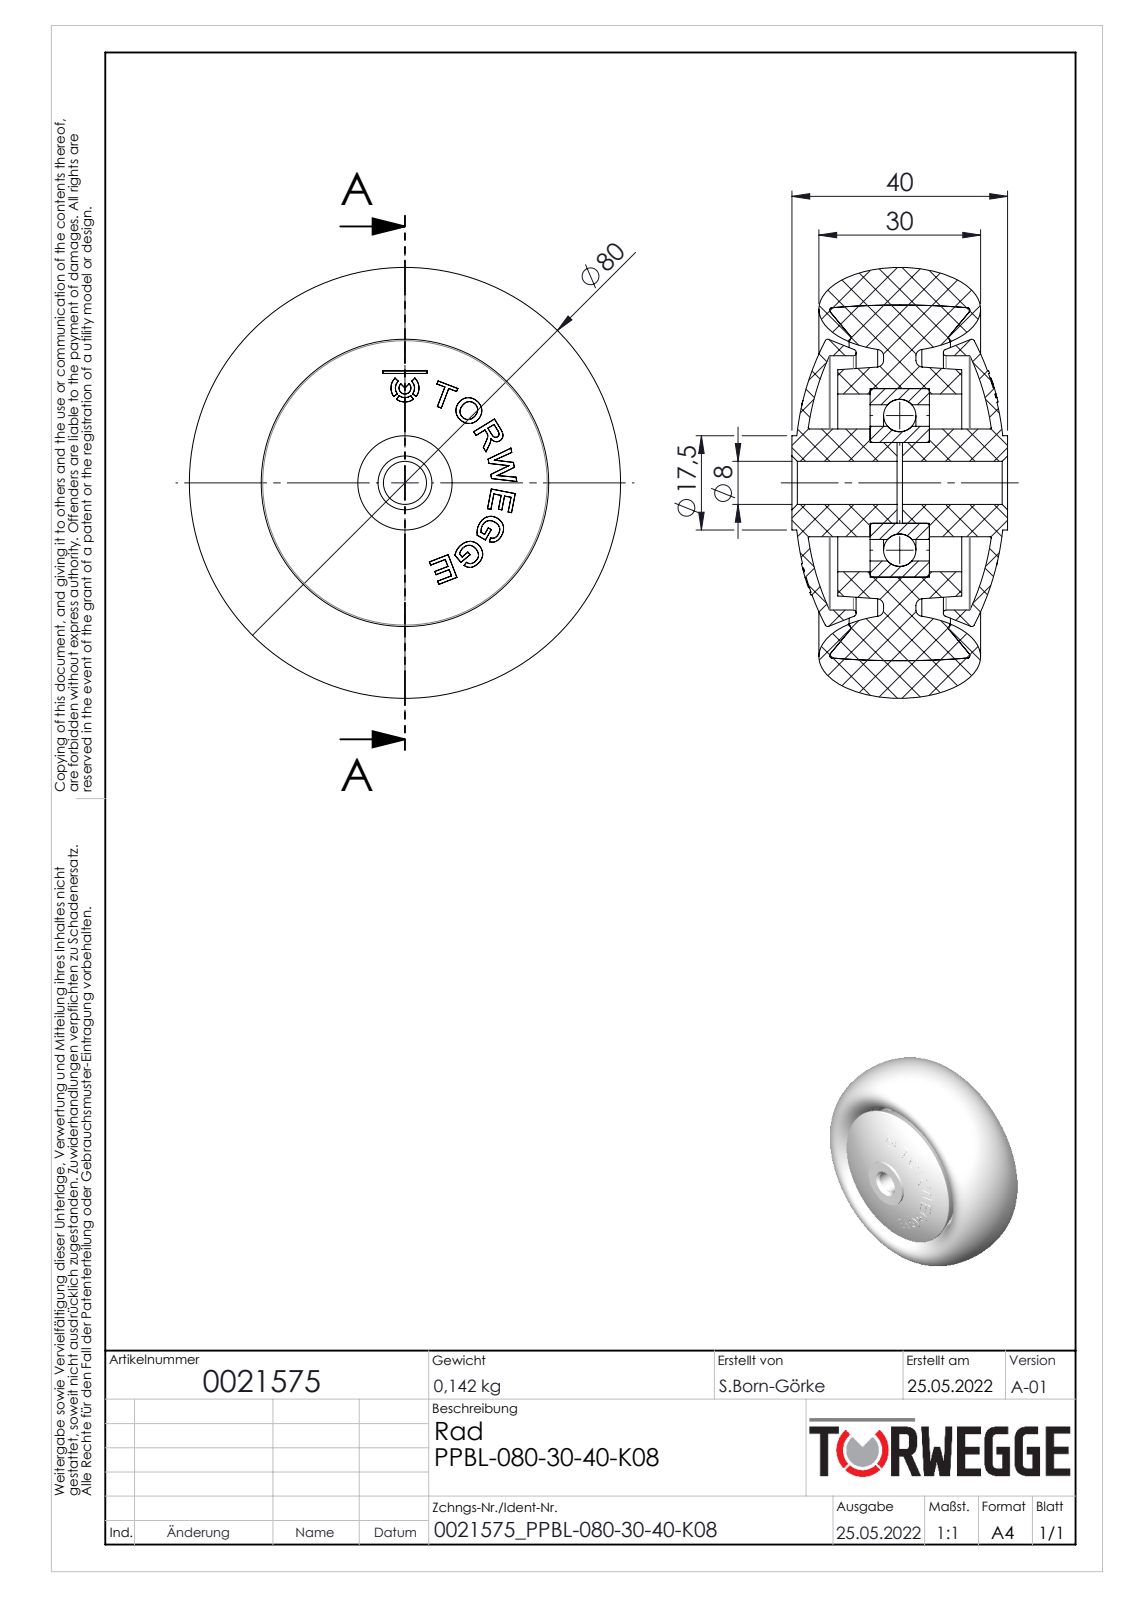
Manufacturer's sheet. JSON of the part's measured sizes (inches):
{"part_name": "0021575", "step_written_by": "SolidWorks 2020 (AUTOMOTIVE_DESIGN)", "units": "inches", "bodies": {"solids": 6, "faces": 398, "planar": 18, "cylindrical": 38, "other": 342}, "overall_size": [3.15, 3.137, 1.575], "volume_in3": 7.003, "surface_area_in2": 63.95, "round_holes": [[0.315, 1], [1.142, 1], [1.299, 1], [1.378, 1], [1.858, 1]], "round_bosses_or_shafts": [[0.827, 1], [0.787, 1], [0.689, 1], [0.591, 1]], "face_to_face_distances": [0.236, 0.669, 0.335, 0.433, 0.906, 0.571, 0.098, 1.004, 1.24, 0.768]}
